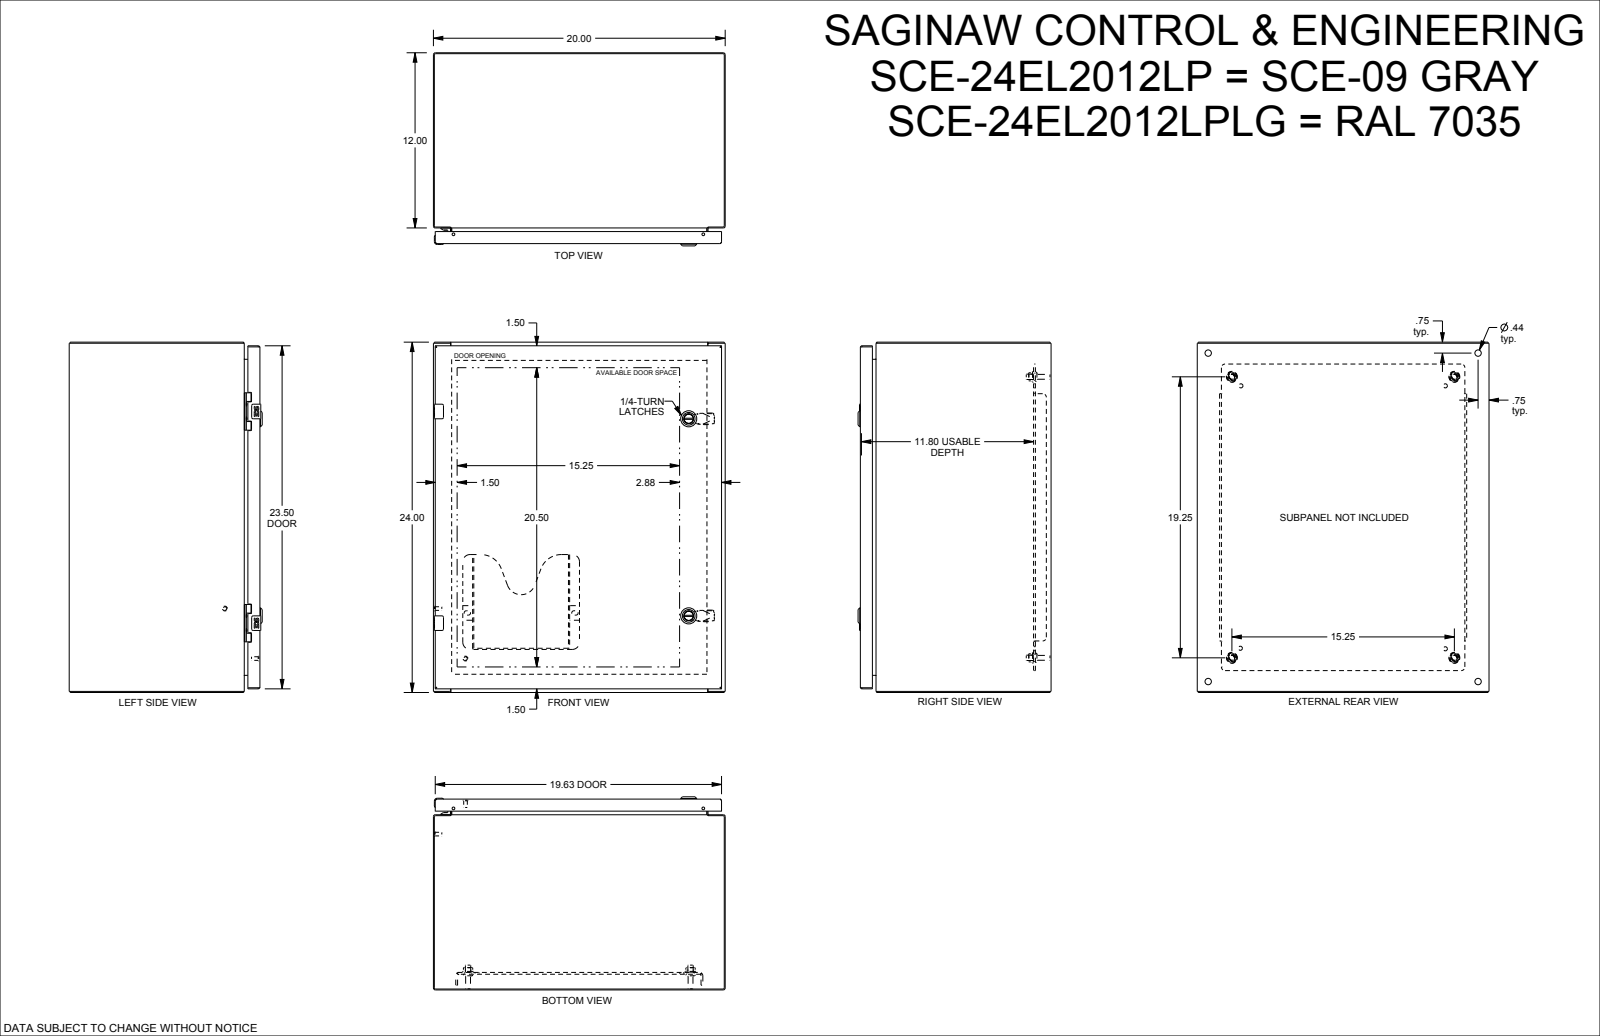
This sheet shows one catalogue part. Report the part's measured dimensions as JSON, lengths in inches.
{"part_name": "SCE-24EL2012LP", "step_written_by": "SolidWorks 2021 (AUTOMOTIVE_DESIGN)", "units": "inches", "bodies": {"solids": 45, "faces": 2787, "planar": 1089, "cylindrical": 840, "other": 858}, "overall_size": [24, 20, 13.23], "volume_in3": 225.8, "surface_area_in2": 5525, "round_holes": [[0.172, 4], [0.205, 4], [0.244, 4], [0.266, 4], [0.281, 4], [0.367, 4], [0.375, 4], [0.437, 4], [0.5, 4], [0.04, 2], [0.188, 2], [0.197, 2]], "round_bosses_or_shafts": [[0.17, 6], [0.366, 4], [0.332, 4], [0.25, 4], [0.248, 4], [0.24, 4], [0.196, 3], [1.102, 2]], "partial_cylinders_radius": [[0.012, 56], [0.01, 28], [0.015, 24], [0.02, 20], [0.04, 17], [0.06, 13], [0.029, 12], [0.1, 12]], "face_to_face_distances": [0.075, 19.925, 0.06, 23.925, 13.073, 12.998, 13.013, 12.938, 1, 0.125], "hole_center_spacings": [0.985, 14.5, 0.02, 0.493, 0.494, 0.875, 2.298, 4.493]}
